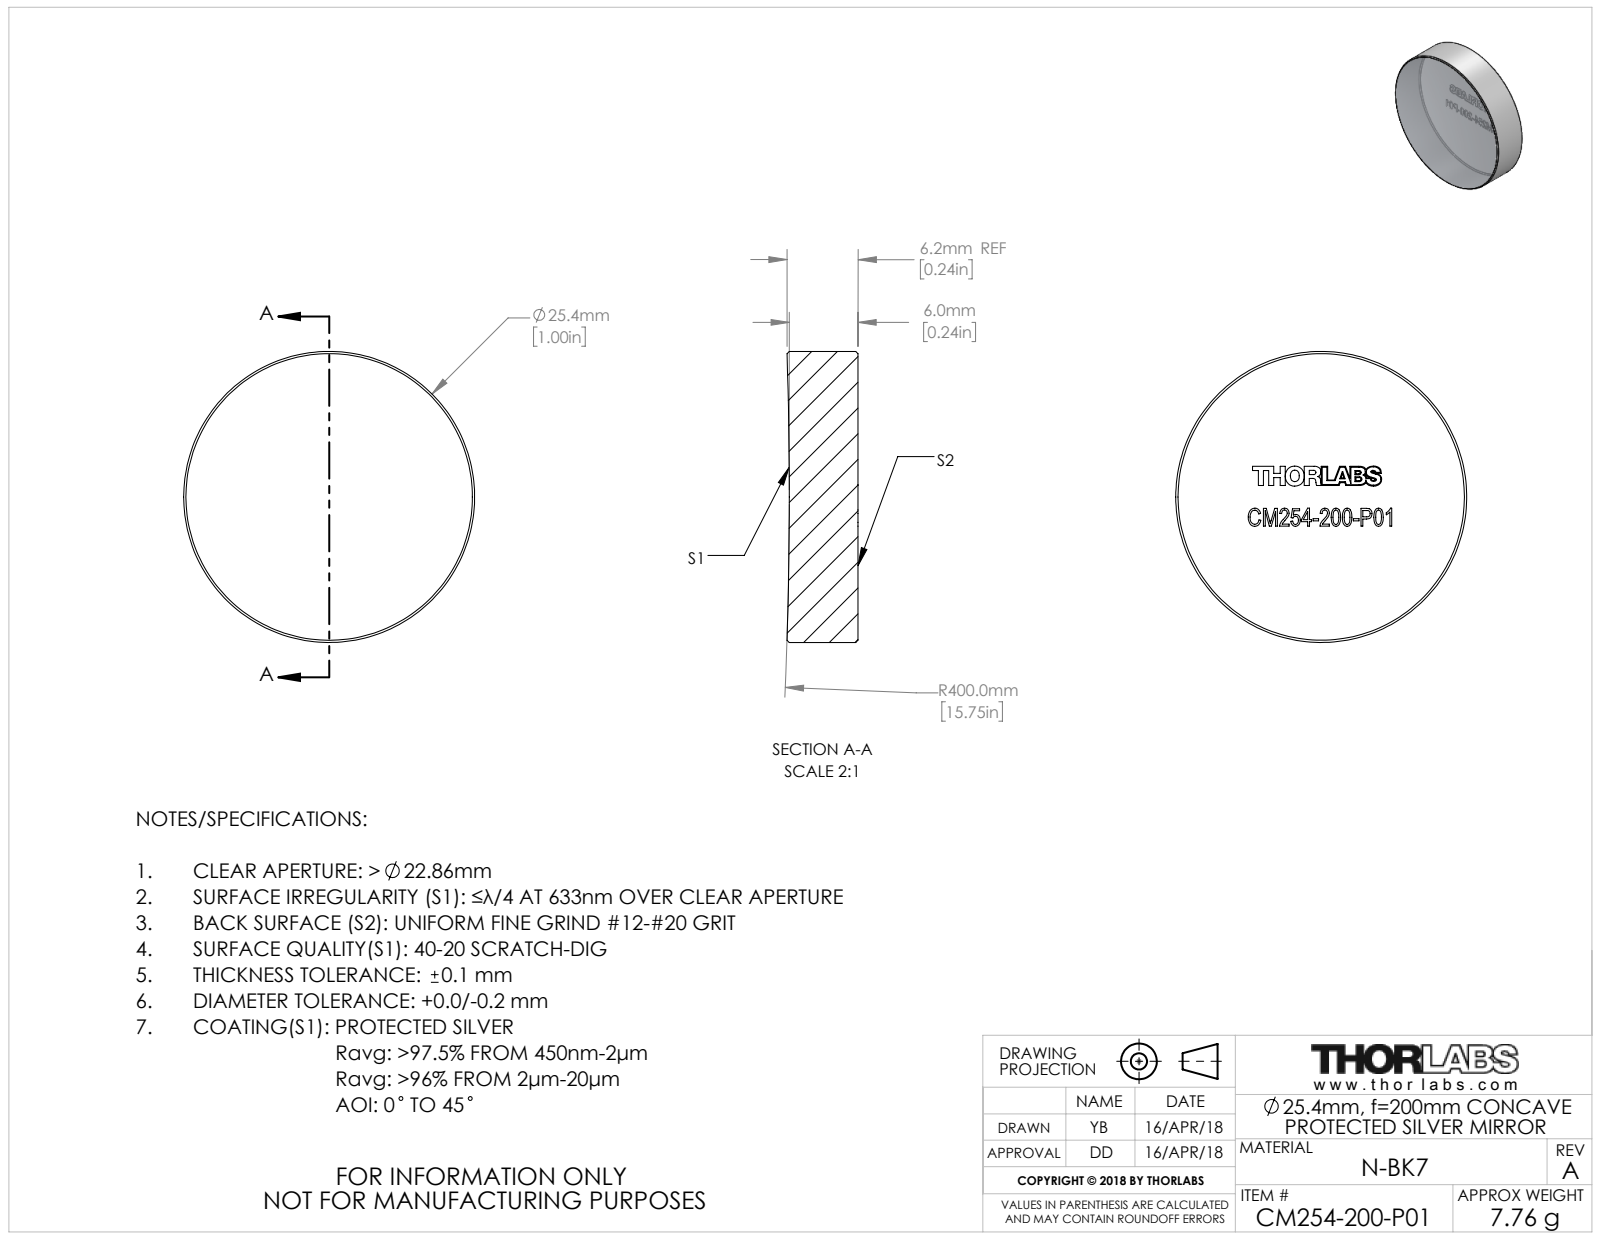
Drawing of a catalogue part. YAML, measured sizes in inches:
part_name: "TTN153284-E0W"
step_written_by: "SolidWorks 2018 (CONFIG_CONTROL_DESIGN)"
units: inches
bodies: {solids: 1, faces: 42, planar: 34, cylindrical: 2, other: 6}
overall_size: [1, 1, 0.244]
volume: 0.188
surface_area: 2.308
round_bosses_or_shafts:
  - {diameter: 1, count: 1}
